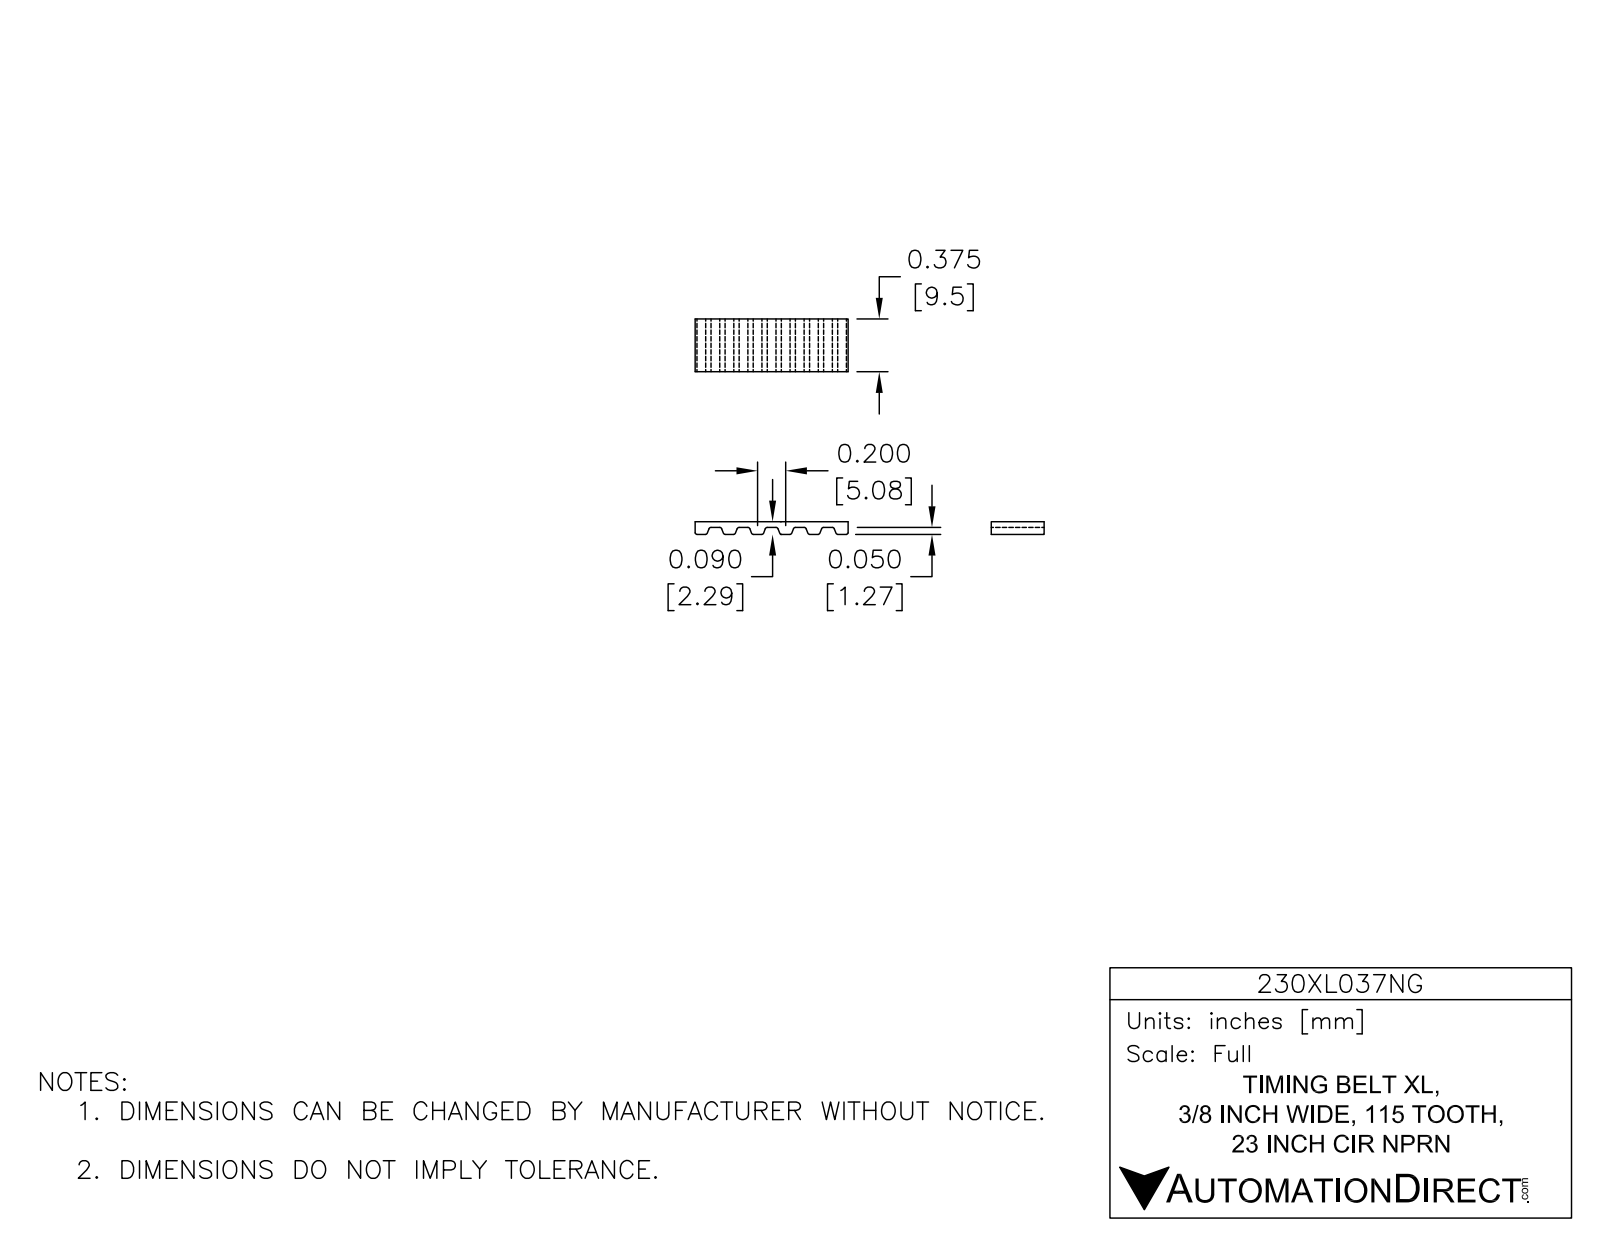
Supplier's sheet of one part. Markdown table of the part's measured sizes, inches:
| quantity | value |
| --- | --- |
| part name | 230XL037NG |
| STEP written by | SolidWorks 2014 (AUTOMOTIVE_DESIGN) |
| units | inches |
| bodies | 1 solid, 960 faces (418 planar, 542 cylindrical, 0 other) |
| overall size | 9.788 × 3 × 0.375 |
| volume | 0.469 in³ |
| surface area | 22.04 in² |
| partial cylindrical surfaces (radius × count) | 0.015 × 460, 1.46 × 2, 1.5 × 2 |
| main face-to-face distances | 3, 0.04, 2.96, 0.375, 2.92, 0.09, 2.91, 0.05, 2.87, 0.179 |
